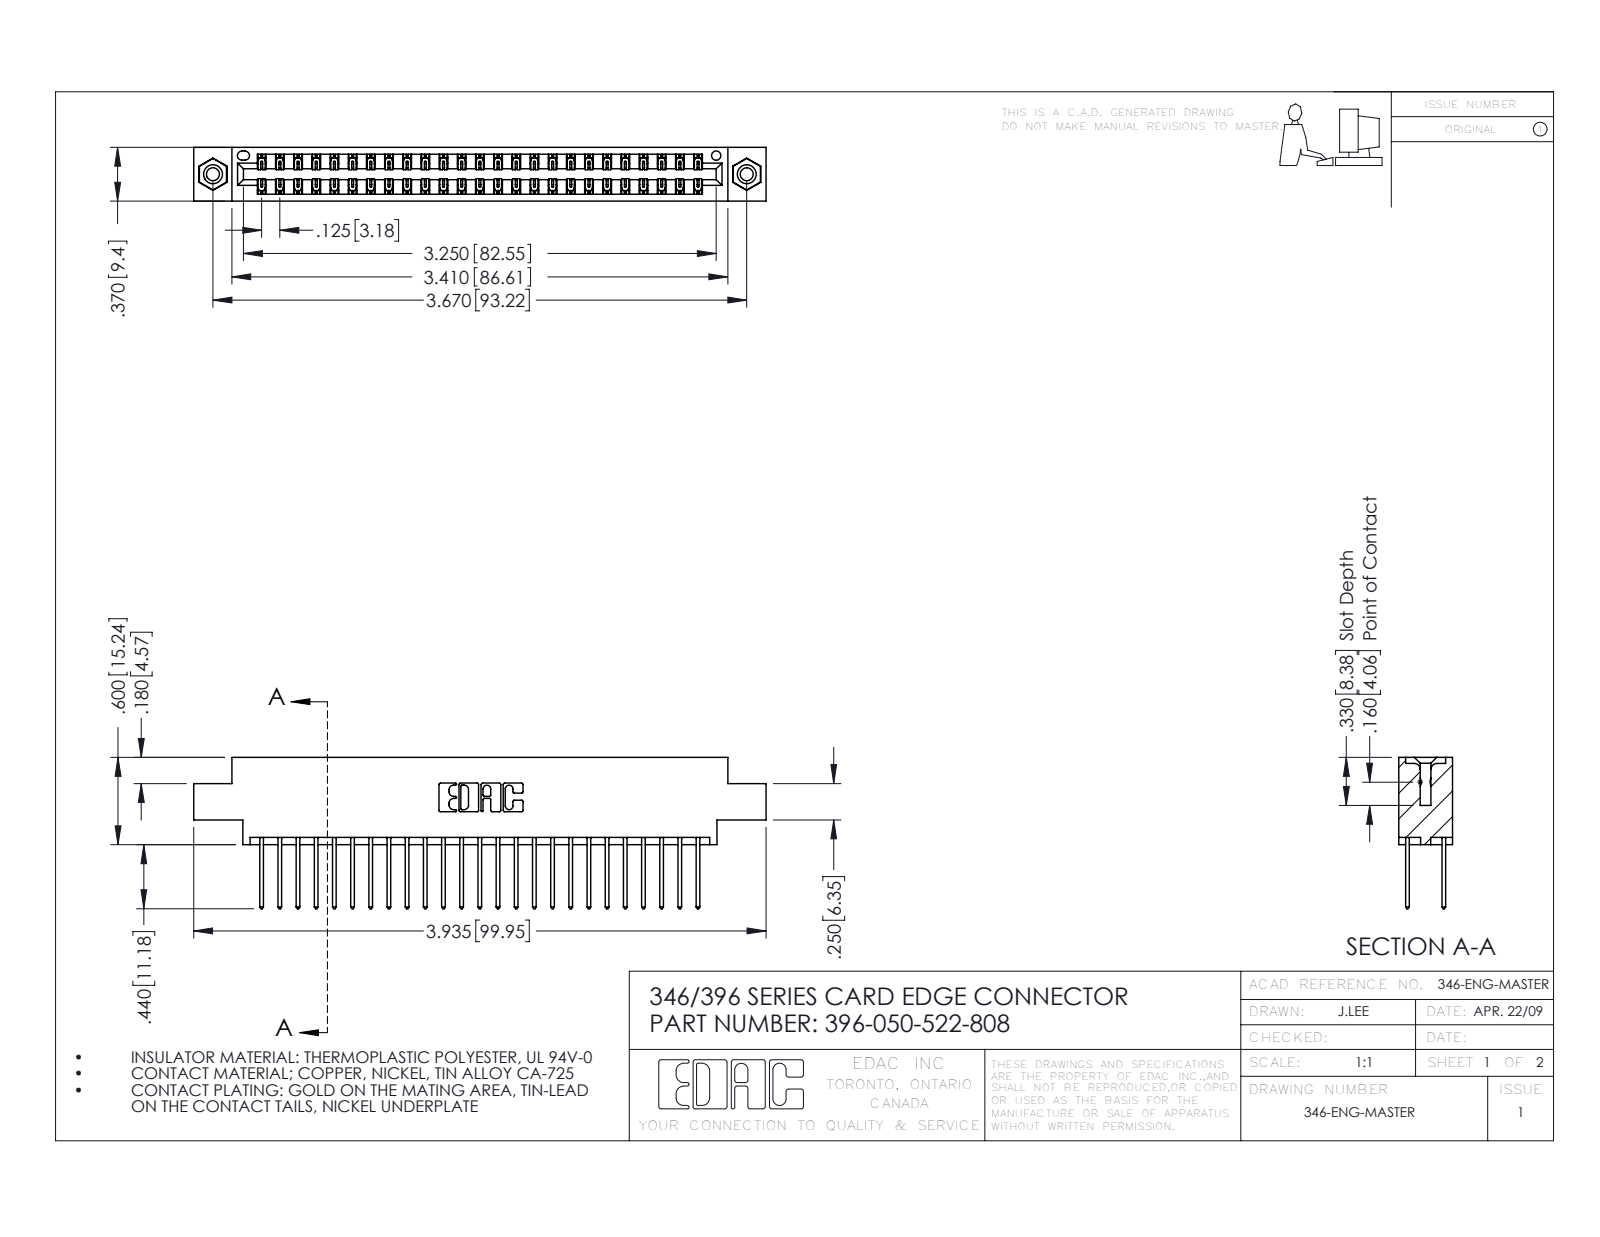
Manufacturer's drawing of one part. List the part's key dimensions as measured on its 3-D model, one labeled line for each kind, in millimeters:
Part name (STEP PRODUCT): 345-292-001_345-293-122; 346 Part_0.170 Offset - 0.156 Dia-TI; 345-250-001_345-250-003-102; 396-050-522-808
STEP written by: SolidWorks 2016 (CONFIG_CONTROL_DESIGN)
Units: millimetres
Bodies: 53 solids, 2786 faces (1862 planar, 908 cylindrical, 16 other)
Overall size (bounding box): 99.9 × 26.4 × 9.4
Volume: 9 590 mm³ · Surface area: 13 700 mm²
Round holes (diameter × count): ⌀2.3 ×2, ⌀3.2 ×2, ⌀4 ×2, ⌀1.6 ×1
Round bosses / shafts (diameter × count): ⌀3.9 ×2
Partial cylindrical surfaces — rounded edges, fillets, slot ends (radius × count): R0.2 ×75, R0.3 ×50, R0.3 ×22, R0.2 ×6, R0.8 ×6, R0.7 ×3, R0.4 ×2, R0.6 ×2
Main face-to-face distances: 1.2, 8.2, 6.4, 9.4, 1.8, 7.6, 0.6, 7, 5.6, 3.8
Hole centre spacings: 6.2, 87.9, 93.2
